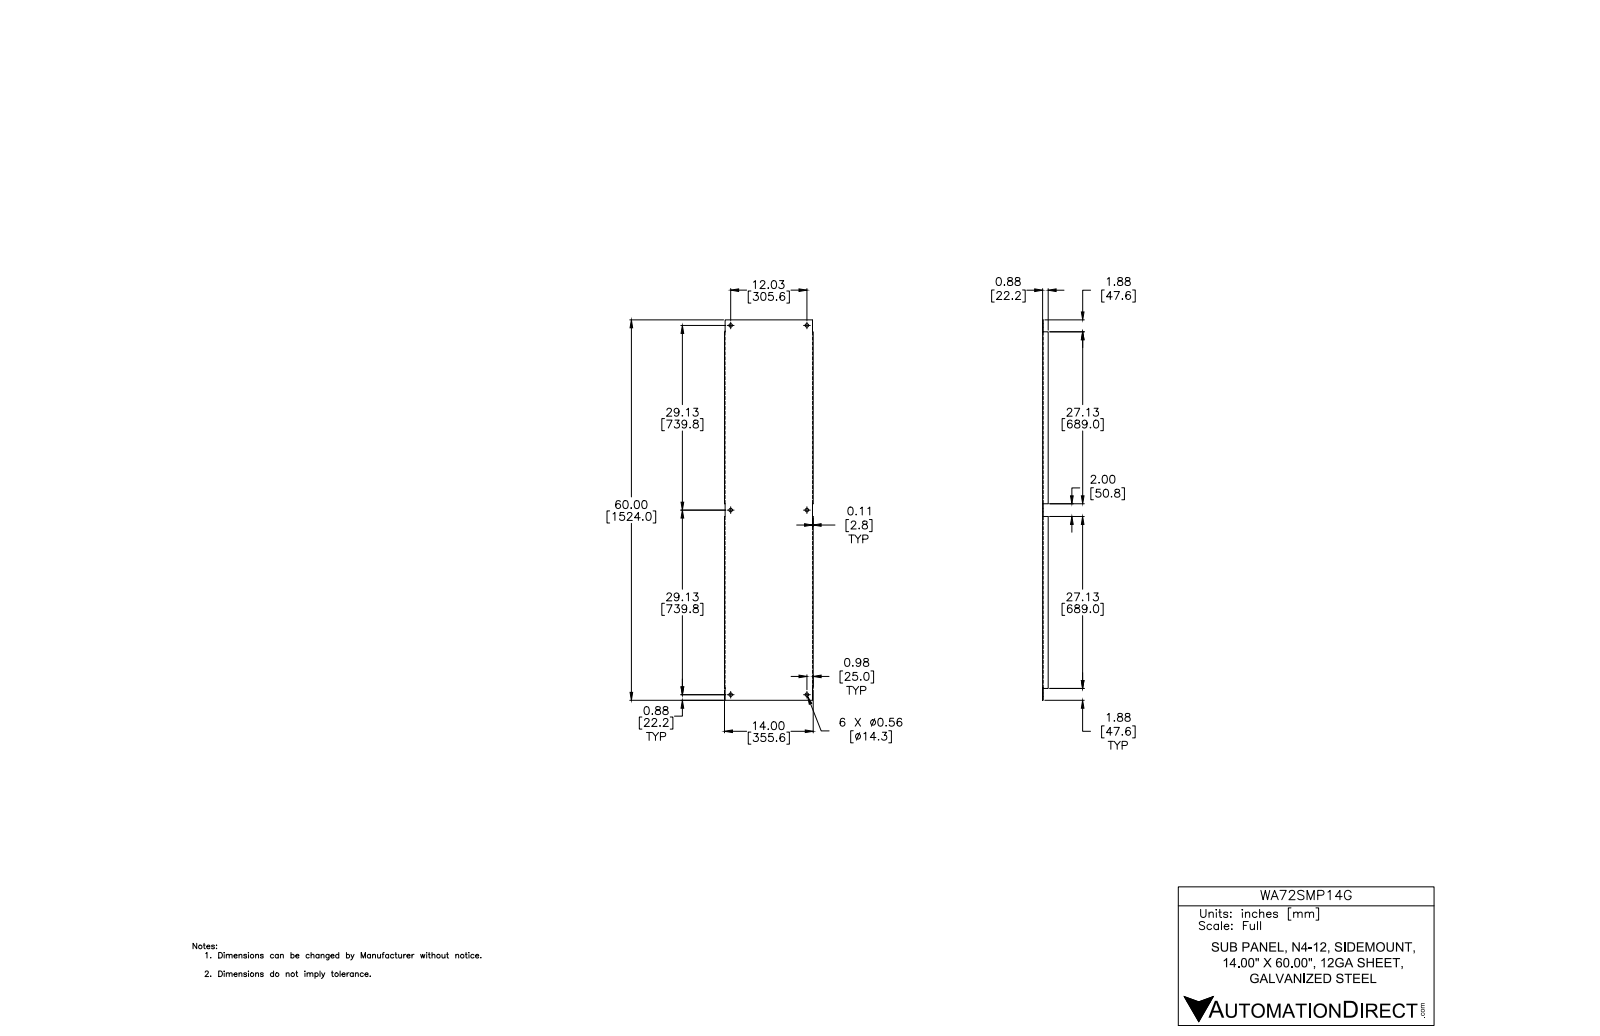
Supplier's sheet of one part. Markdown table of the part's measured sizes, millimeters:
| quantity | value |
| --- | --- |
| part name | WA60SMP14G-WA90SMP20G |
| STEP written by | Autodesk Inventor 2012 (AUTOMOTIVE_DESIGN) |
| units | millimeters |
| bodies | 1 solid, 48 faces (34 planar, 14 cylindrical, 0 other) |
| overall size | 1524 × 355.6 × 22.2 |
| volume | 1 412 000 mm³ |
| surface area | 1 196 000 mm² |
| round holes (diameter × count) | 14.3 × 6 |
| partial cylindrical surfaces (radius × count) | 0.4 × 2, 2.8 × 2 |
| main face-to-face distances | 2.4, 353.2, 350.9, 355.6, 19.8, 22.2, 1524, 2.8, 352.8, 0.4 |
| hole center spacings | 739.8, 800.4, 305.6, 1479.6, 1510.8 |
